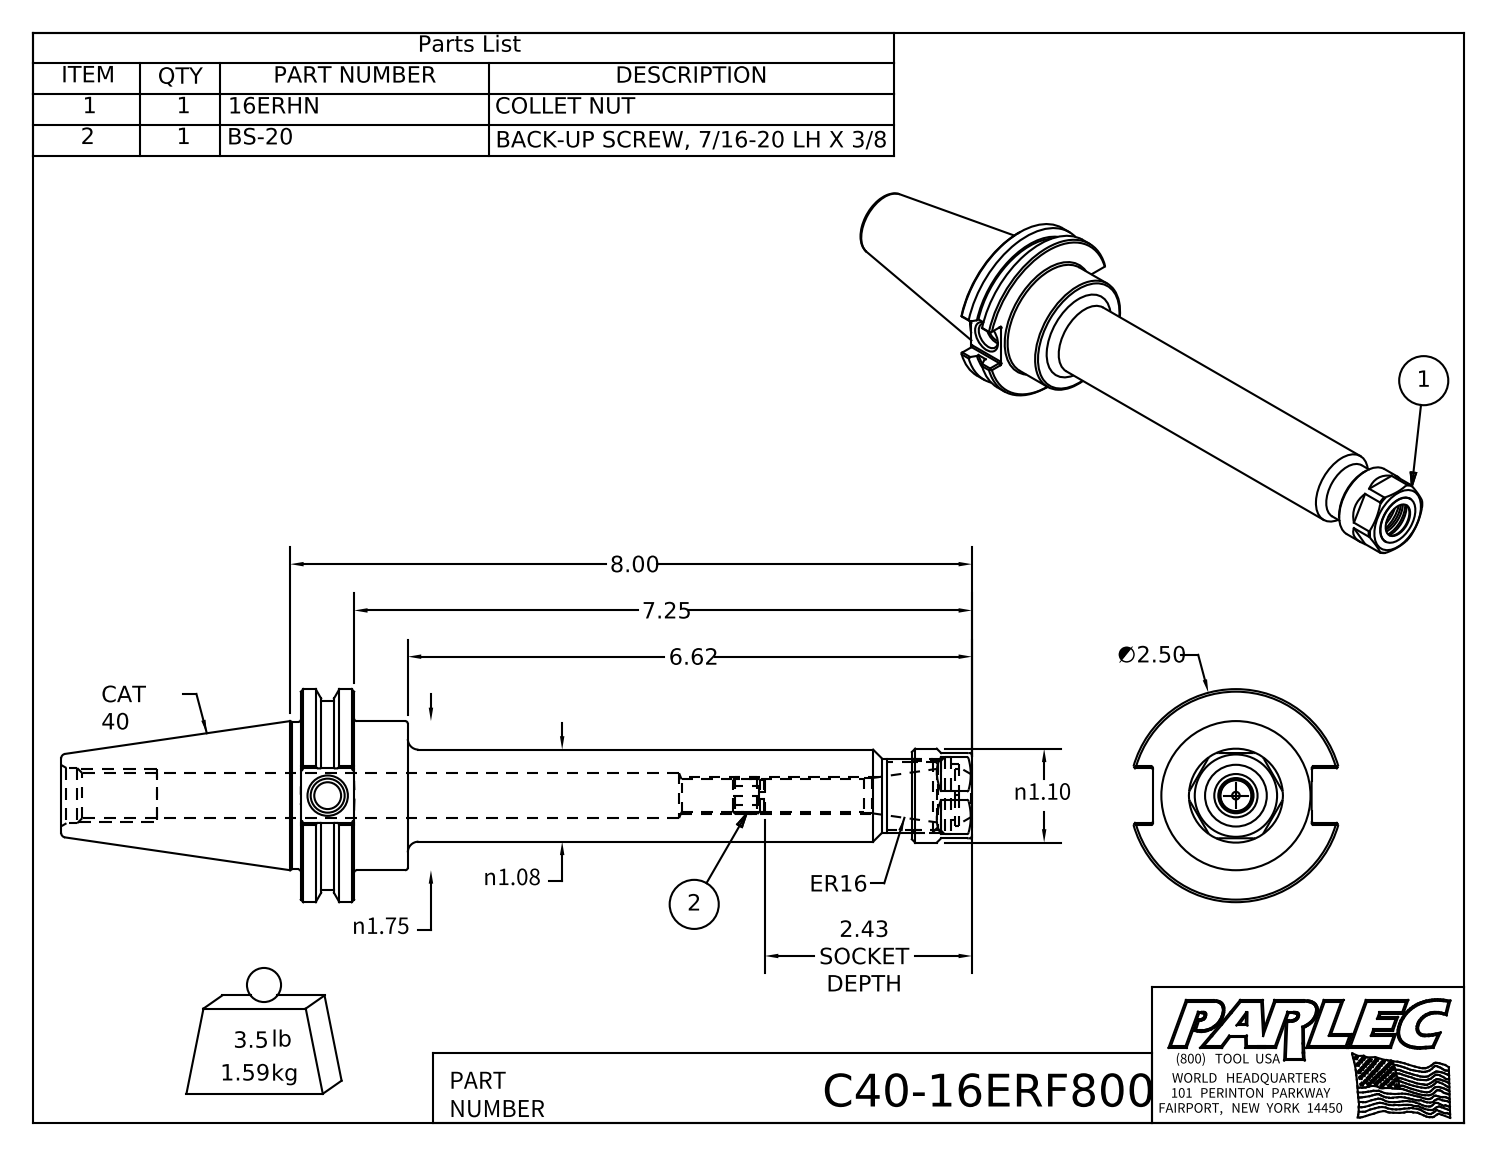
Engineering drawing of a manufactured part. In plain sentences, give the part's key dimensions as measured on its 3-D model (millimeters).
The part is named "C40-16ER8-1; 16ERHN; BS-20; C40-16ERF800". Its 3-D file was written by "Autodesk Inventor 2016 (AUTOMOTIVE_DESIGN)". It is 3 solids with 137 faces: 59 planar, 39 cylindrical and 39 other. Overall it measures 271.46 by 63.5 by 61.05 millimeters. Its volume is 199 558 cubic millimeters and its surface area 46 171 square millimeters. Round holes: 1 of diameter 2.29, 1 of diameter 8, 1 of diameter 9.73, 1 of diameter 10.13, 1 of diameter 10.5, 1 of diameter 12.4, 1 of diameter 13.38, 1 of diameter 13.39, 1 of diameter 16.46, 1 of diameter 17.02, 1 of diameter 20.5, 1 of diameter 23. Round bosses or shafts: 1 of diameter 63.5, 1 of diameter 56.36, 1 of diameter 44.45, 1 of diameter 43.94, 1 of diameter 28, 1 of diameter 27.43, 1 of diameter 22, 1 of diameter 10.97. Partial cylindrical surfaces (rounded edges, fillets, slot ends): 12 of radius 0.51, 1 of radius 7.24, 1 of radius 9. The main face-to-face distances are 15.88, 31.88, 16, 200.03, 184.15, 168.15, 25.14, 4.44, 20.7, 194.33. The hole center spacings are 1.52.
